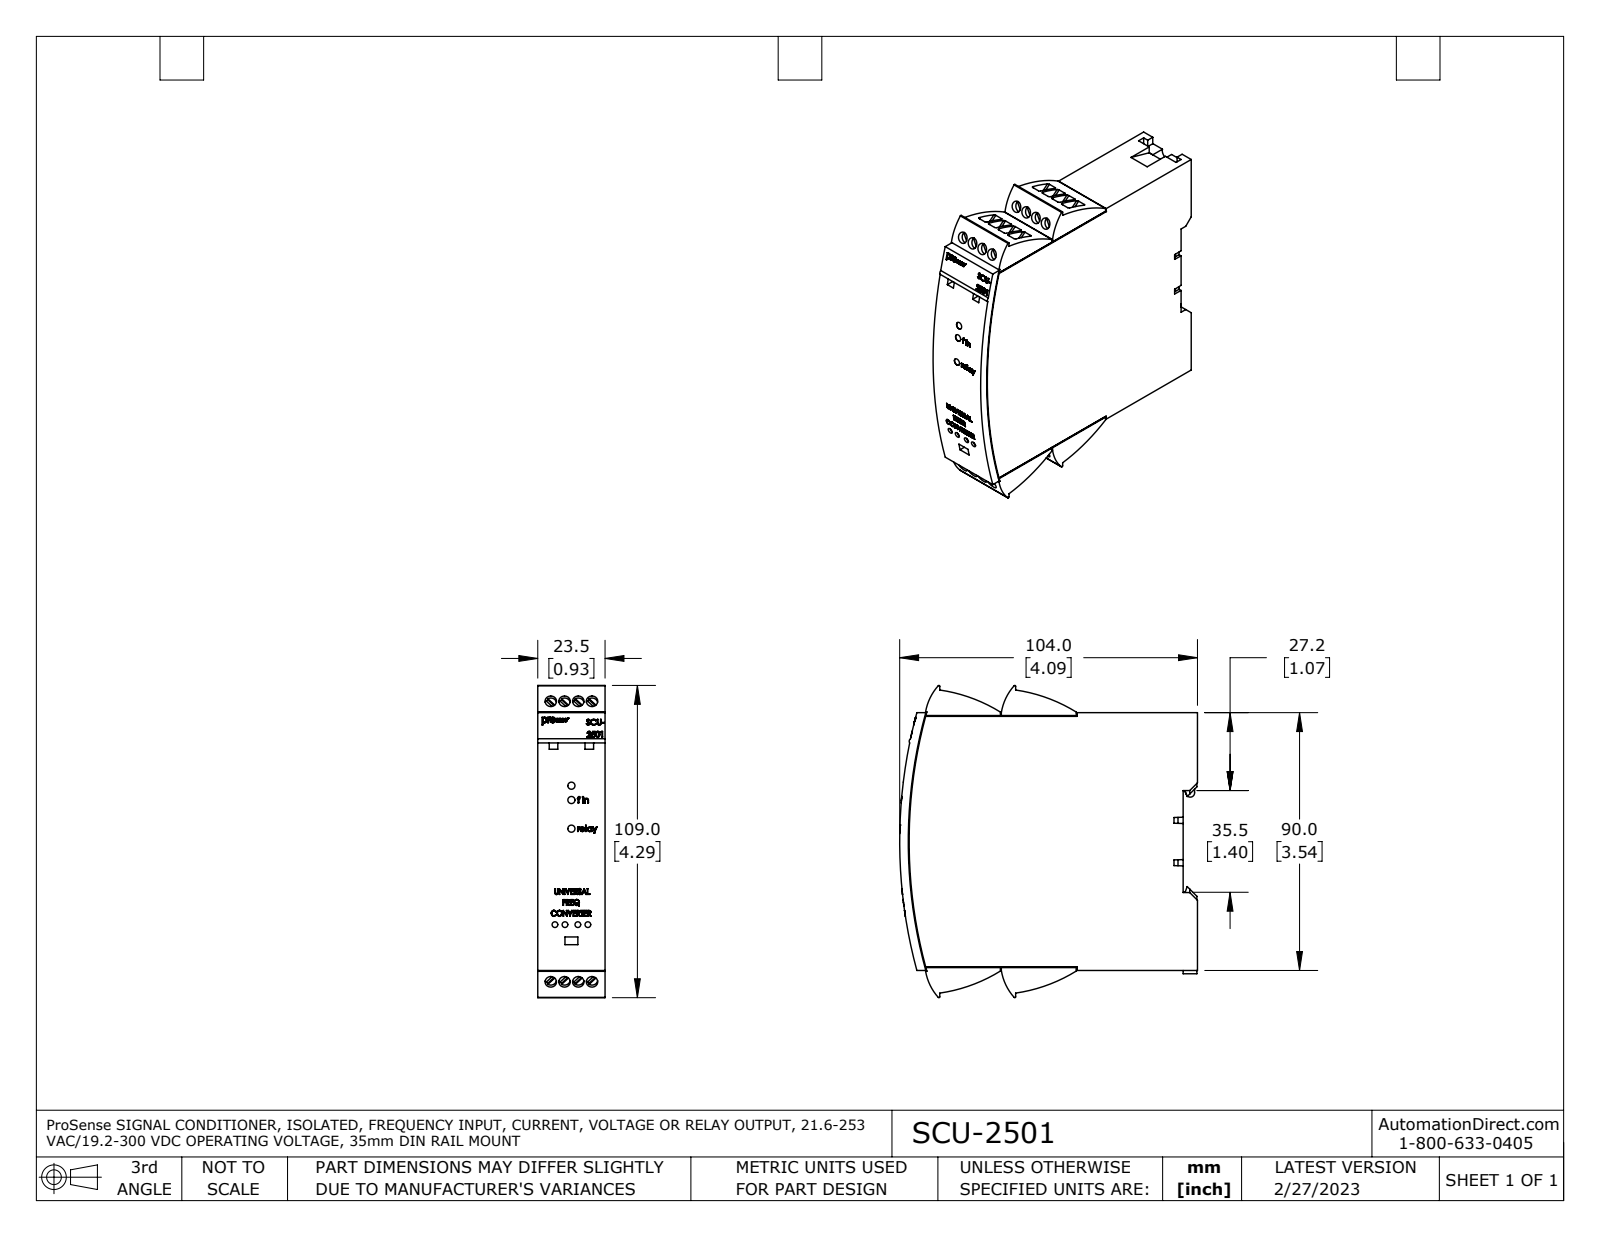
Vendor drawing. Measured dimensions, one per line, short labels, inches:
name: SCU-2501 from 4000_6000_9000 Complete asm nc m1E FP MOD1 fxt
written by: SolidWorks 2021 (AUTOMOTIVE_DESIGN)
unit: in
bodies: 3 solids, 1258 faces (731 planar, 243 cylindrical, 284 other)
size: 4.291 × 4.094 × 0.925
volume: 13.36 in³; area: 55.45 in²
holes: 16× ⌀0.157, 4× ⌀0.079, 4× ⌀0.091, 3× ⌀0.098
bosses: 2× ⌀0.079
rounds: 69× R0.02, 4× R0.012, 4× R0.04, 4× R0.726, 4× R2.175, 3× R0.059, 3× R0.098, 2× R0.03
face distances: 0.925, 3.543, 0.098, 0.189, 0.187, 0.071, 0.197, 0.118, 0.091, 0.061
hole spacings: 0.189, 0.435, 0.378, 0.391, 0.544, 0.567, 0.689, 0.138
